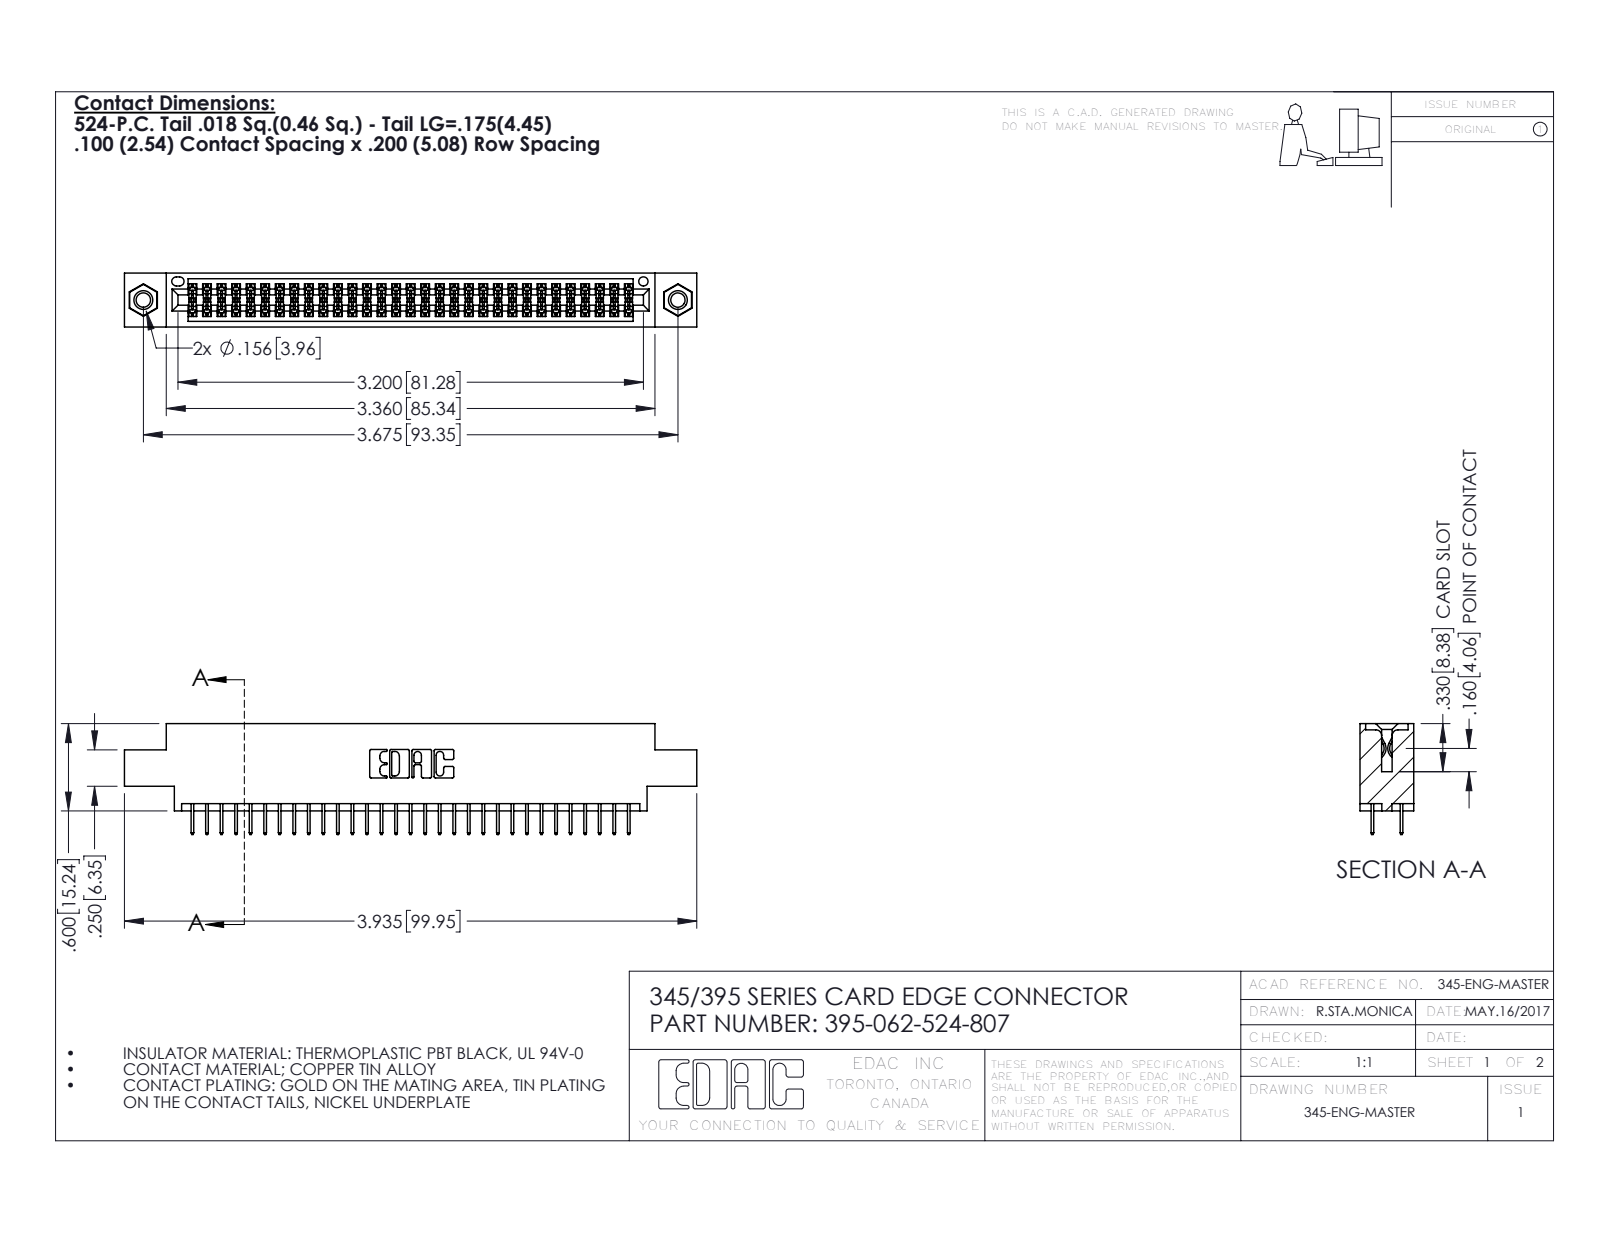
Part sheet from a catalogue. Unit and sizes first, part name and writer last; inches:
Units: inches
Overall size (bounding box): 3.935 × 0.762 × 0.37
Round holes (diameter × count): ⌀0.098 ×2, ⌀0.125 ×2, ⌀0.156 ×2, ⌀0.064 ×1
Round bosses / shafts (diameter × count): ⌀0.155 ×2
Partial cylindrical surfaces — rounded edges, fillets, slot ends (radius × count): R0.006 ×93, R0.01 ×22, R0.007 ×6, R0.031 ×6, R0.026 ×3, R0.014 ×2, R0.019 ×2, R0.022 ×2
Main face-to-face distances: 0.072, 0.298, 0.37, 0.2, 0.098, 0.272, 0.025, 0.225, 0.175, 0.072
Hole centre spacings: 0.27, 3.44, 3.675
Volume: 0.573 in³ · Surface area: 21.06 in²
Bodies: 65 solids, 3538 faces (2534 planar, 988 cylindrical, 16 other)
Part name (STEP PRODUCT): 345-250-001_345-250-005-103; 345-292-001_345-293-124; 345 Part_0.170 Offset - 0.156 Dia-TI; 395-062-524-807
STEP written by: SolidWorks 2016 (CONFIG_CONTROL_DESIGN)
